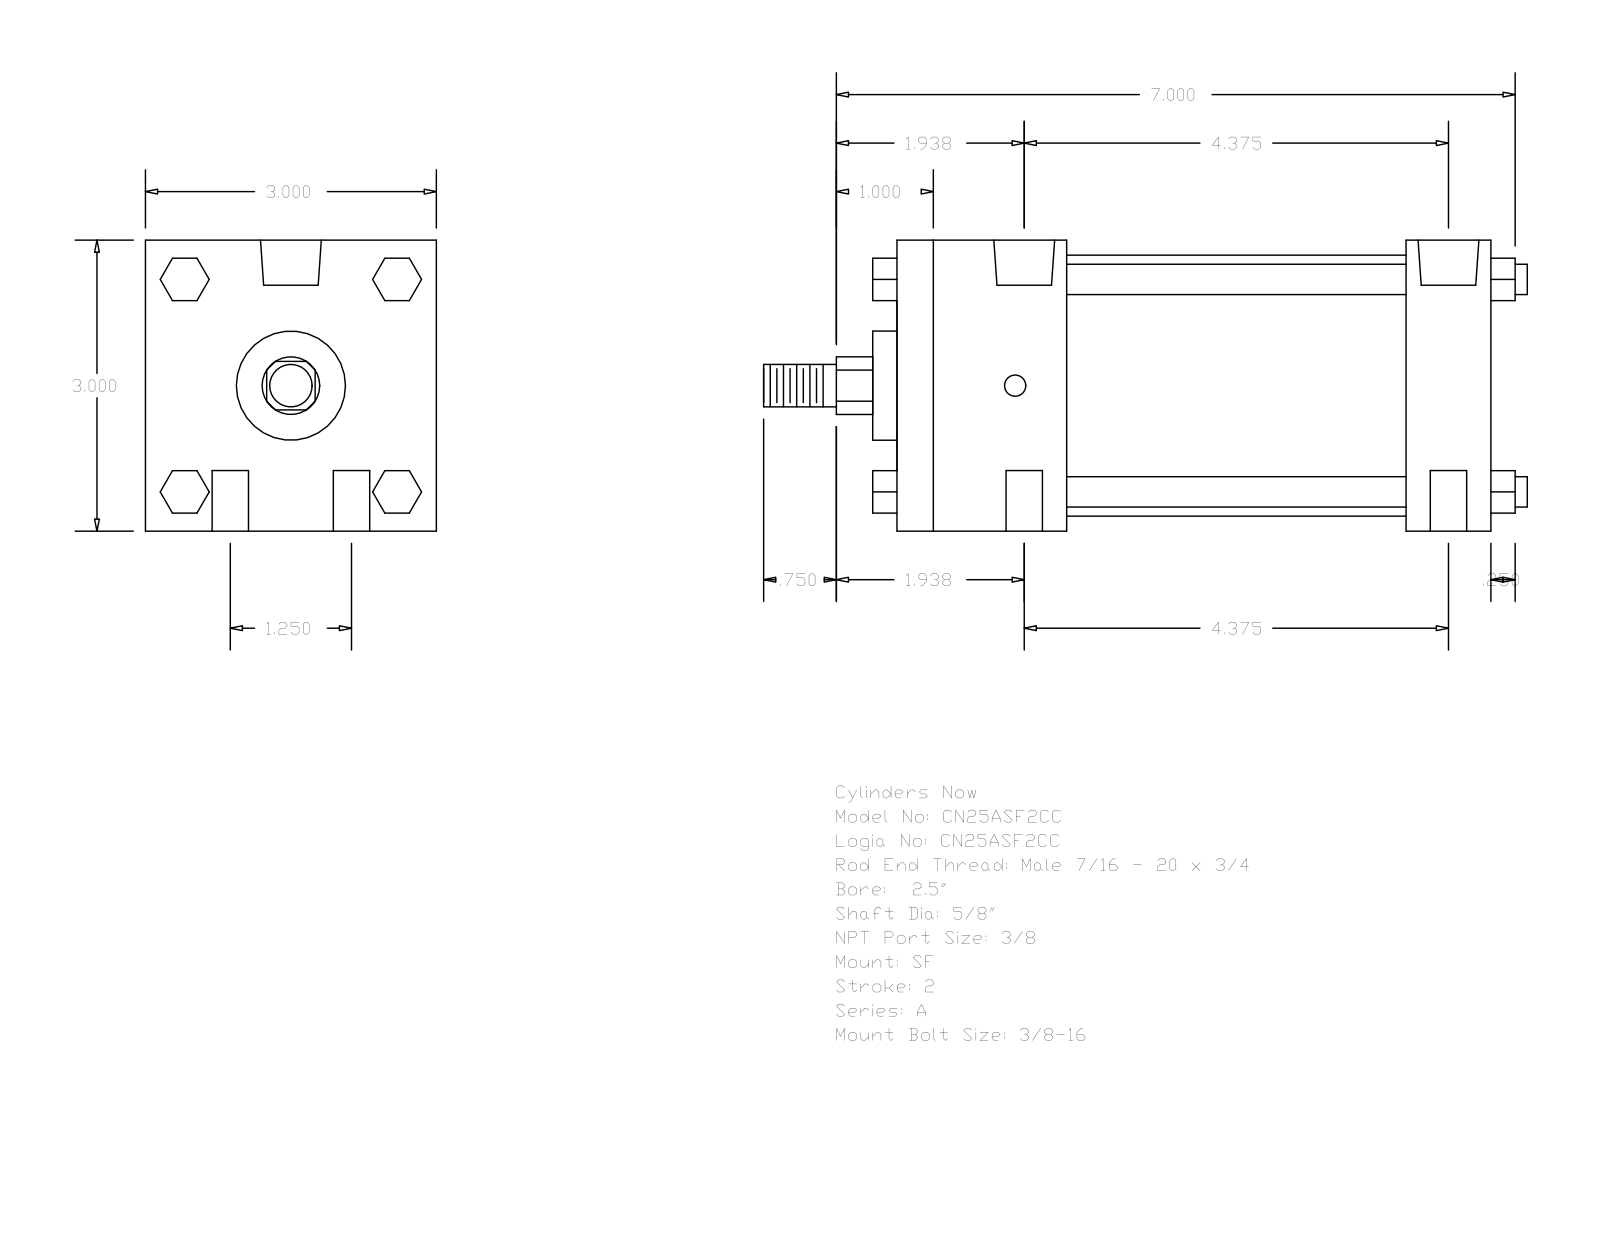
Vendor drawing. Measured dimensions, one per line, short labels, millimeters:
name: A_SF__0250_0.625
written by: GSSL Pune (CONFIG_CONTROL_DESIGN)
unit: mm
bodies: 0 solids, 124 faces (94 planar, 30 cylindrical, 0 other)
size: 200.03 × 76.2 × 76.2
holes: 4× ⌀9.53, 2× ⌀5.56, 2× ⌀15.93
bosses: 4× ⌀7.94, 1× ⌀68.33, 1× ⌀28.57, 1× ⌀15.88, 1× ⌀11.11
rounds: 1× R7.54
face distances: 76.2, 155.57, 44.45, 133.34, 22.23, 88.89, 111.12, 6.35, 161.92, 50.8
hole spacings: 15.88, 112.26, 111.13, 31.76, 115.58, 115.89
